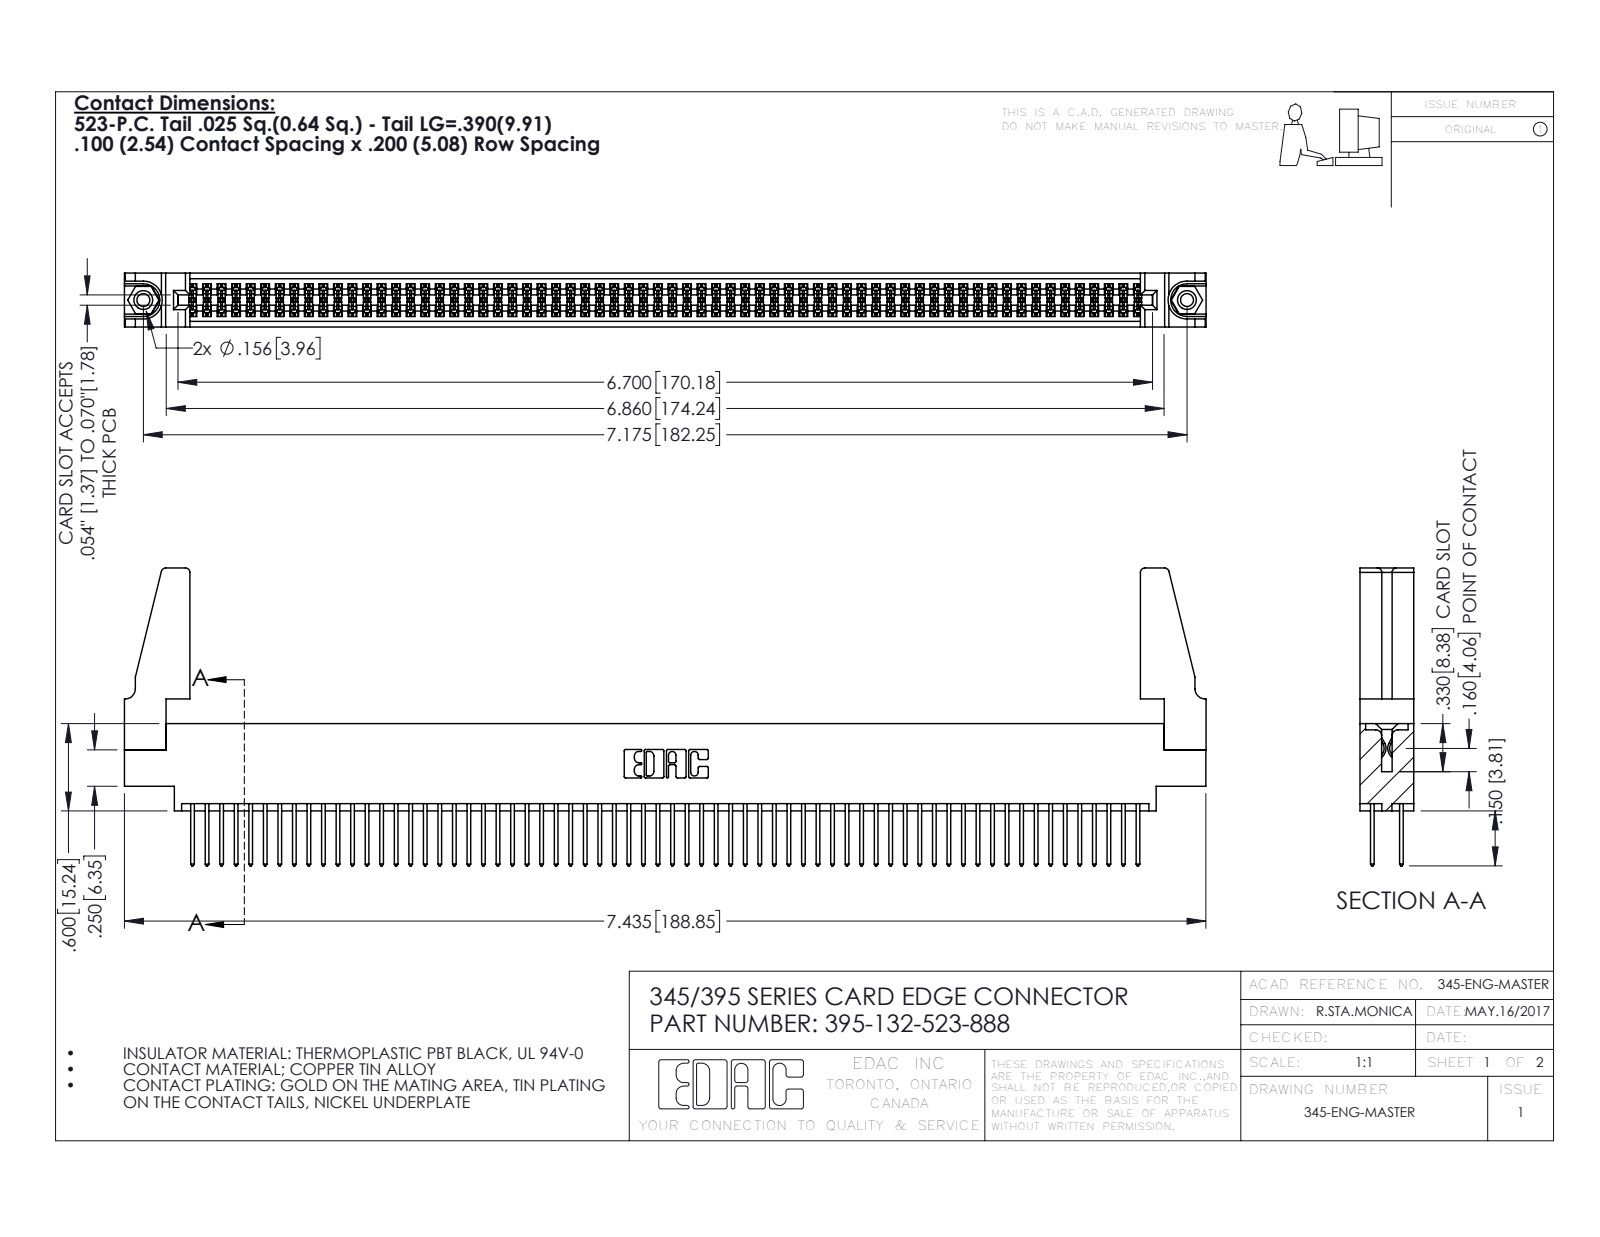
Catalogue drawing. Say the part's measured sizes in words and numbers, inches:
The part is named "345-250-001_345-250-001-102; 395-132-523-888; 345 Part_0.170 Offset - 0.156 Dia-TH; 345-220-078_345-220-088 (+1 more)". Its 3-D file was written by "SolidWorks 2016 (CONFIG_CONTROL_DESIGN)". It is 137 solids with 6854 faces: 4512 planar, 2326 cylindrical and 16 other. Overall it measures 7.436 by 2.047 by 0.37 inches. Its volume is 1.341 cubic inches and its surface area 50.57 square inches. Round holes: 2 of diameter 0.089, 2 of diameter 0.125, 2 of diameter 0.156, 1 of diameter 0.064. Round bosses or shafts: 2 of diameter 0.155. Partial cylindrical surfaces (rounded edges, fillets, slot ends): 198 of radius 0.006, 132 of radius 0.01, 22 of radius 0.01, 8 of radius 0.03, 6 of radius 0.007, 6 of radius 0.031, 3 of radius 0.026, 2 of radius 0.014. The main face-to-face distances are 0.072, 0.298, 0.37, 0.098, 0.272, 0.025, 0.2, 0.225, 0.175, 0.149. The hole center spacings are 0.27, 6.939, 7.175.
